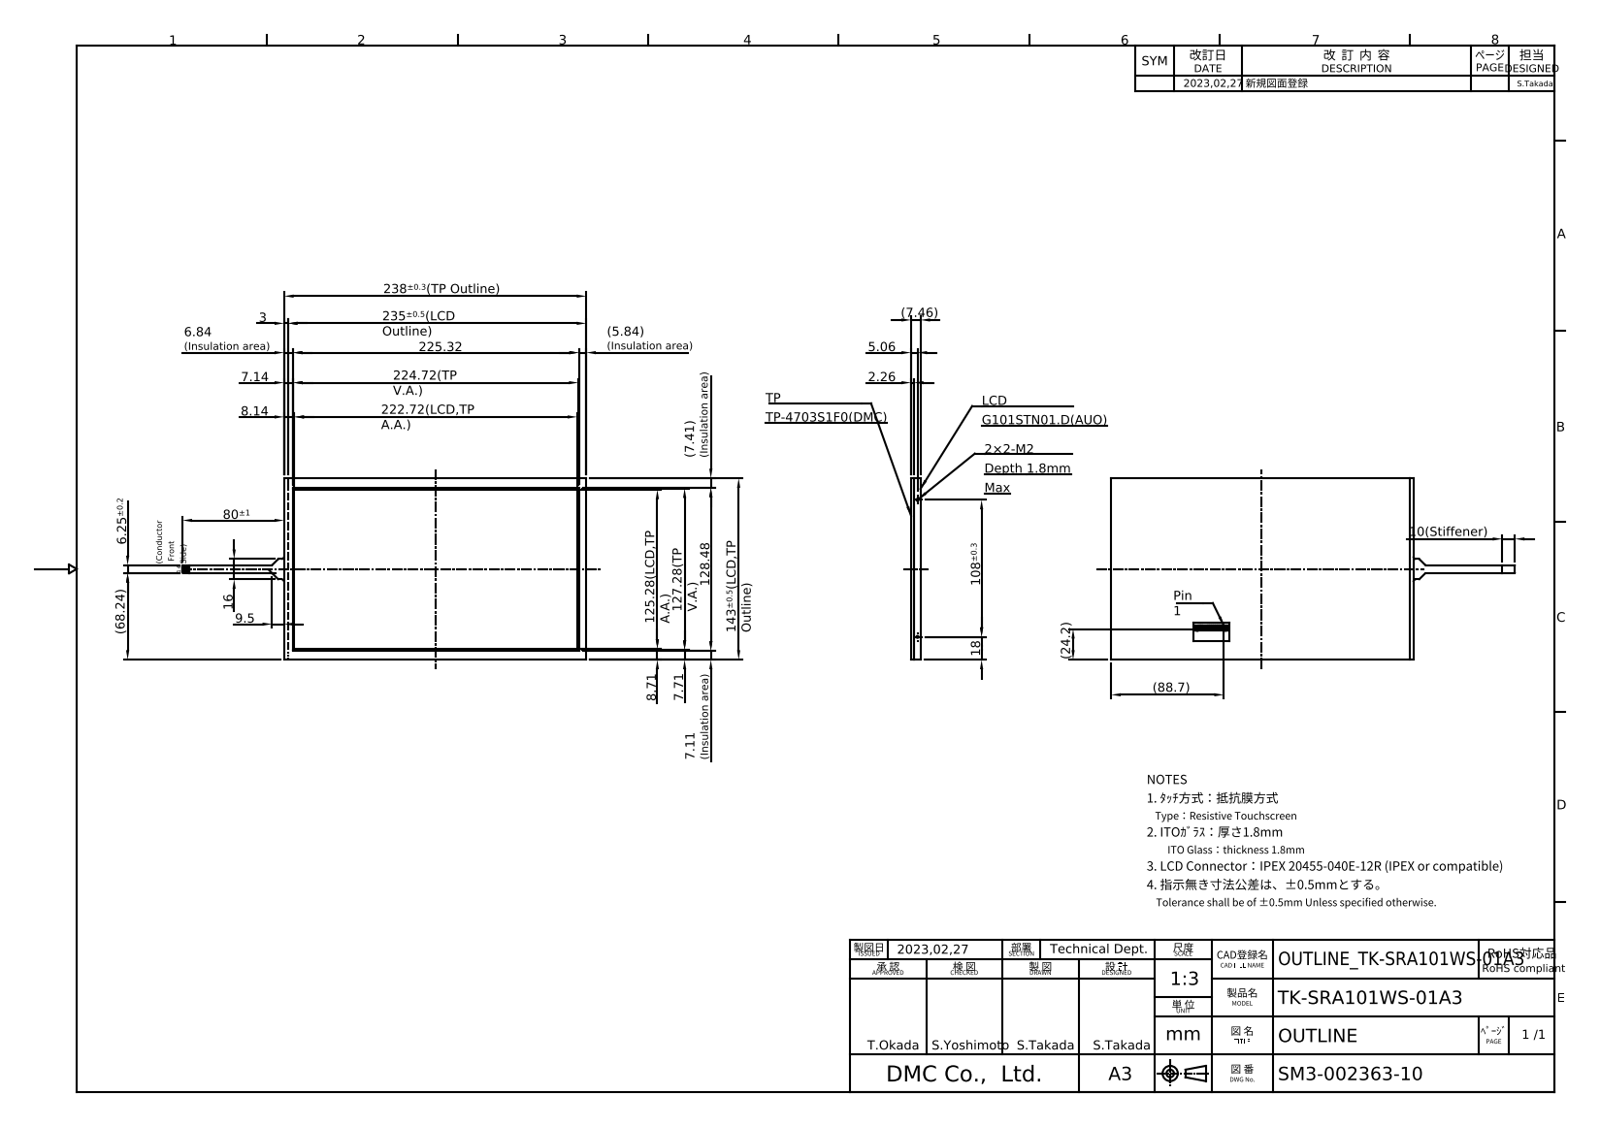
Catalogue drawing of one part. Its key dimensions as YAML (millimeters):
part_name: "HP_TK-SRA101WS-01A3"
step_written_by: "Autodesk Inventor 2020 (AUTOMOTIVE_DESIGN)"
units: millimeters
bodies: {solids: 1, faces: 1670, planar: 1105, cylindrical: 517, other: 48}
overall_size: [318, 143, 7.46]
volume: 246326
surface_area: 136187
round_holes:
  - {diameter: 0.5, count: 2}
  - {diameter: 1.57, count: 2}
partial_cylinders:
  - {radius: 0.1, count: 44}
  - {radius: 0.17, count: 16}
  - {radius: 0.15, count: 9}
  - {radius: 0.2, count: 9}
  - {radius: 0.3, count: 6}
  - {radius: 1, count: 4}
  - {radius: 0.14, count: 2}
  - {radius: 0.22, count: 2}
face_to_face_distances: [7.46, 5.36, 2.1, 2.26, 5.2, 143, 2.36, 5.1, 1, 6.46]
hole_center_spacings: [25.37, 108]
